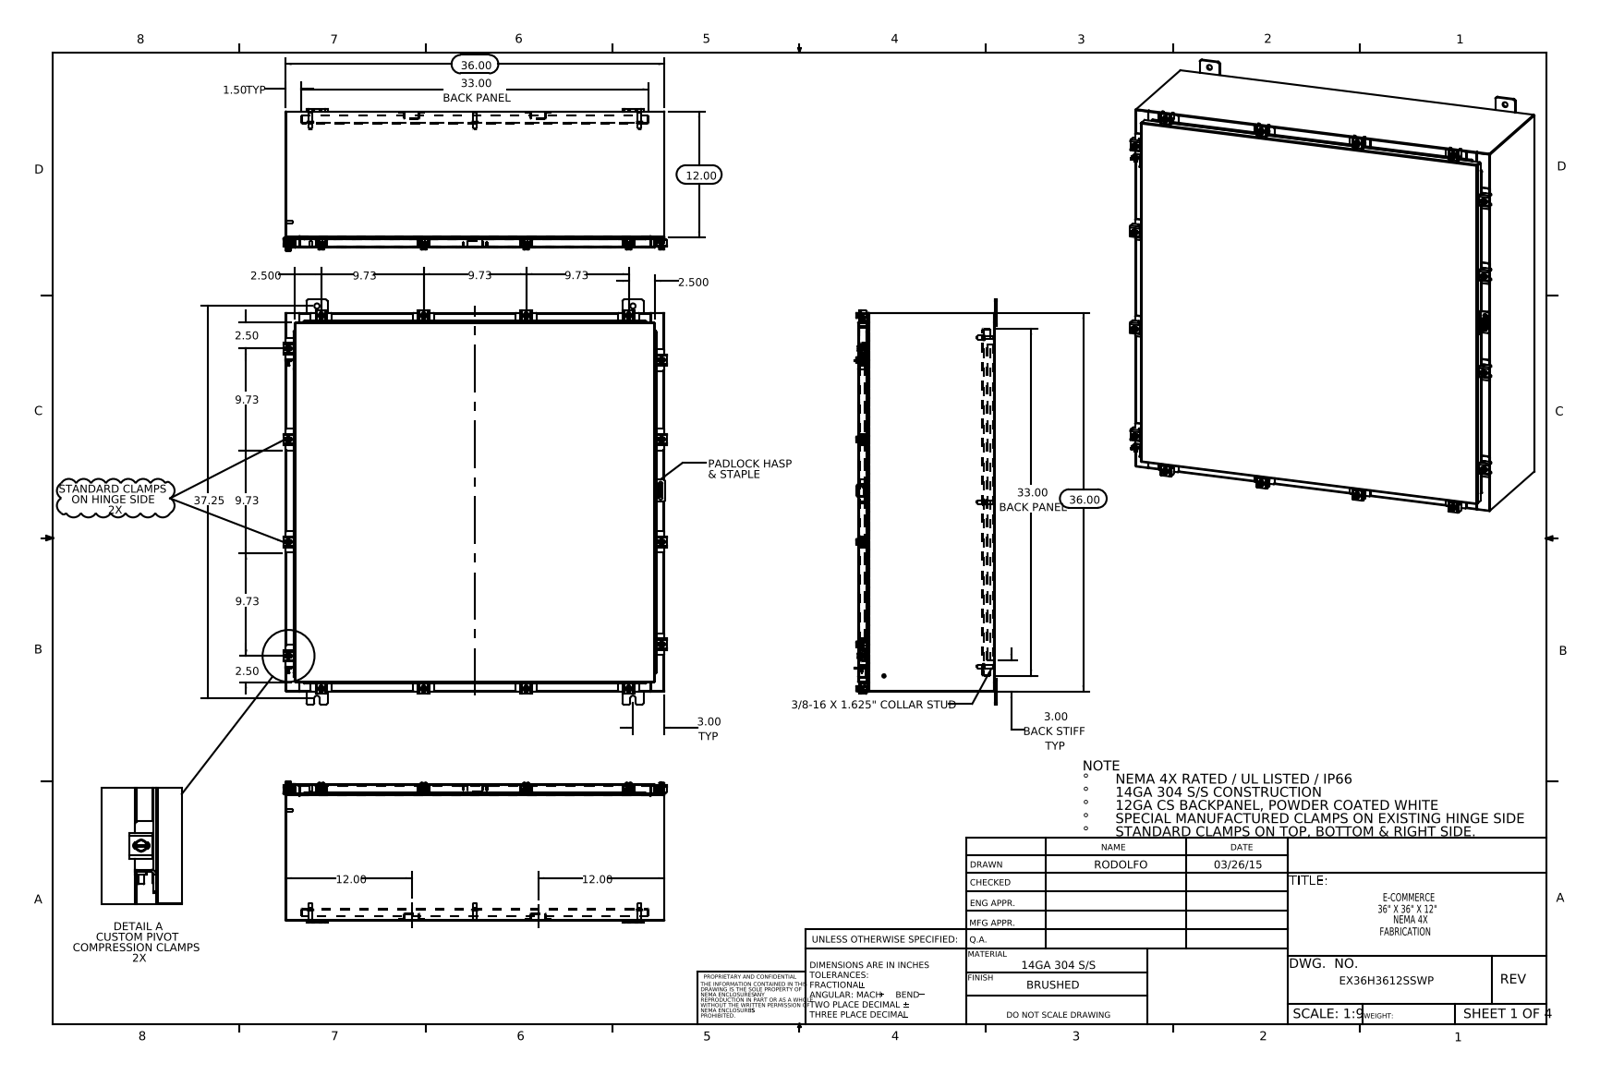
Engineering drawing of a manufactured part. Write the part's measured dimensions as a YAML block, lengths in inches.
part_name: "EX36H3612SSWP Clamp Assembly; EX36H3612SSWP Backpanel; EX36H3612SSWP; EX36H3612SSWP Top (+8 more)"
step_written_by: "SolidWorks 2014 (CONFIG_CONTROL_DESIGN)"
units: inches
bodies: {solids: 114, faces: 2822, planar: 1459, cylindrical: 1083, other: 280}
overall_size: [38.5, 36.421, 13.453]
volume: 504.6
surface_area: 12594
round_holes:
  - {diameter: 0.213, count: 16}
  - {diameter: 0.26, count: 16}
  - {diameter: 0.5, count: 12}
  - {diameter: 0.25, count: 7}
  - {diameter: 0.125, count: 1}
round_bosses_or_shafts:
  - {diameter: 0.5, count: 16}
  - {diameter: 0.25, count: 16}
  - {diameter: 0.399, count: 14}
  - {diameter: 0.625, count: 8}
  - {diameter: 0.375, count: 8}
  - {diameter: 0.33, count: 8}
  - {diameter: 0.157, count: 6}
  - {diameter: 0.14, count: 6}
partial_cylinders:
  - {radius: 0.06, count: 70}
  - {radius: 0.013, count: 38}
  - {radius: 0.088, count: 34}
  - {radius: 0.141, count: 32}
  - {radius: 0.12, count: 30}
  - {radius: 0.19, count: 24}
  - {radius: 0.09, count: 22}
  - {radius: 0.05, count: 21}
face_to_face_distances: [0.075, 12.9, 35.925, 12.826, 12.975, 0.104, 1, 1.075, 11.826, 11.9]
hole_center_spacings: [2.34, 14.744, 15.625, 17.756, 1.969, 5.288, 5.299, 7.043]
